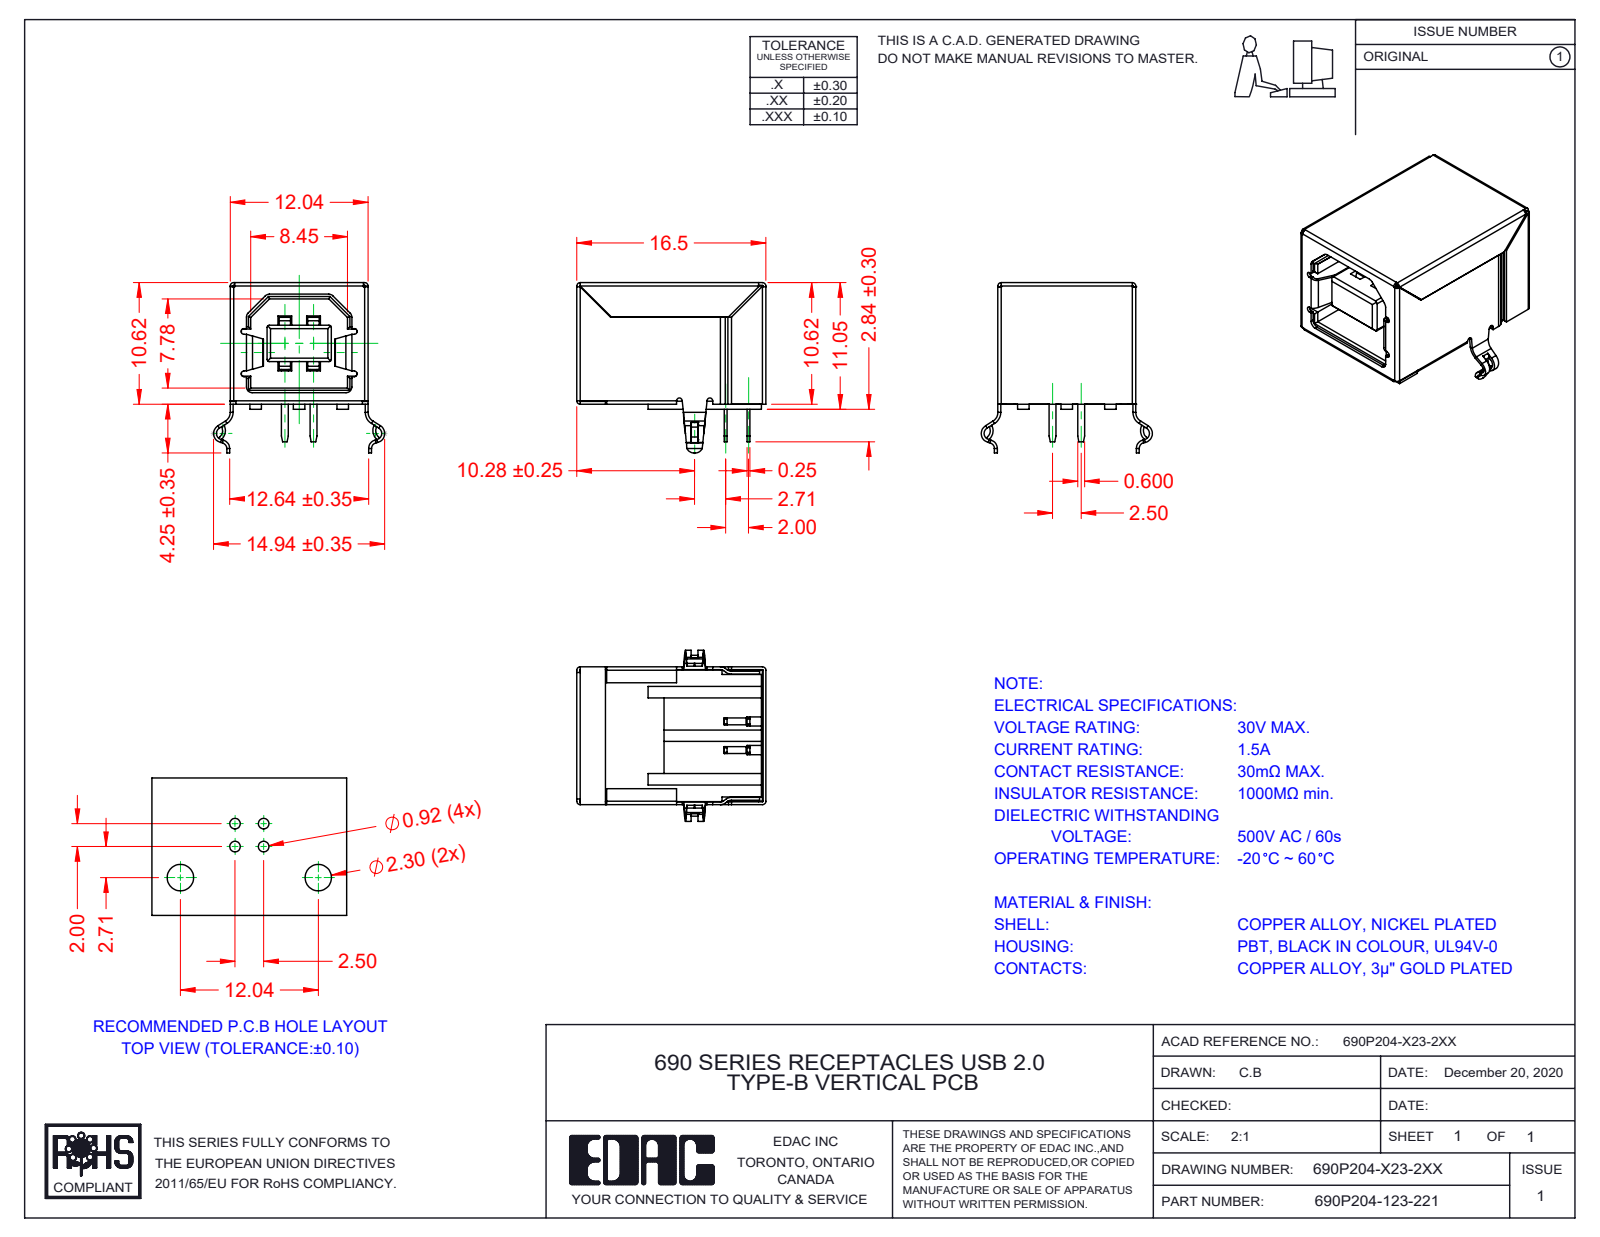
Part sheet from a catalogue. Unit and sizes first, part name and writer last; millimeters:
Units: millimetres
Overall size (bounding box): 16.5 × 14.94 × 14.87
Partial cylindrical surfaces — rounded edges, fillets, slot ends (radius × count): R0.1 ×14, R0.3 ×13, R0.5 ×12, R0.25 ×8, R0.75 ×8, R0.55 ×6, R0.2 ×4, R0.6 ×4
Main face-to-face distances: 11.79, 11.77, 11.52, 10.35, 12.04, 11.54, 10.1, 10.08, 0.38, 10.37
Volume: 1 499 mm³ · Surface area: 3 521 mm²
Bodies: 6 solids, 631 faces (436 planar, 167 cylindrical, 28 other)
Part name (STEP PRODUCT): SHELL 690P204-X23-2XX; CONTACT01 690P204-X23-2XX; CONTACT 690P204-X23-2XX; 690P204-123-211 (+1 more)
STEP written by: SolidWorks 2020 (AUTOMOTIVE_DESIGN)
